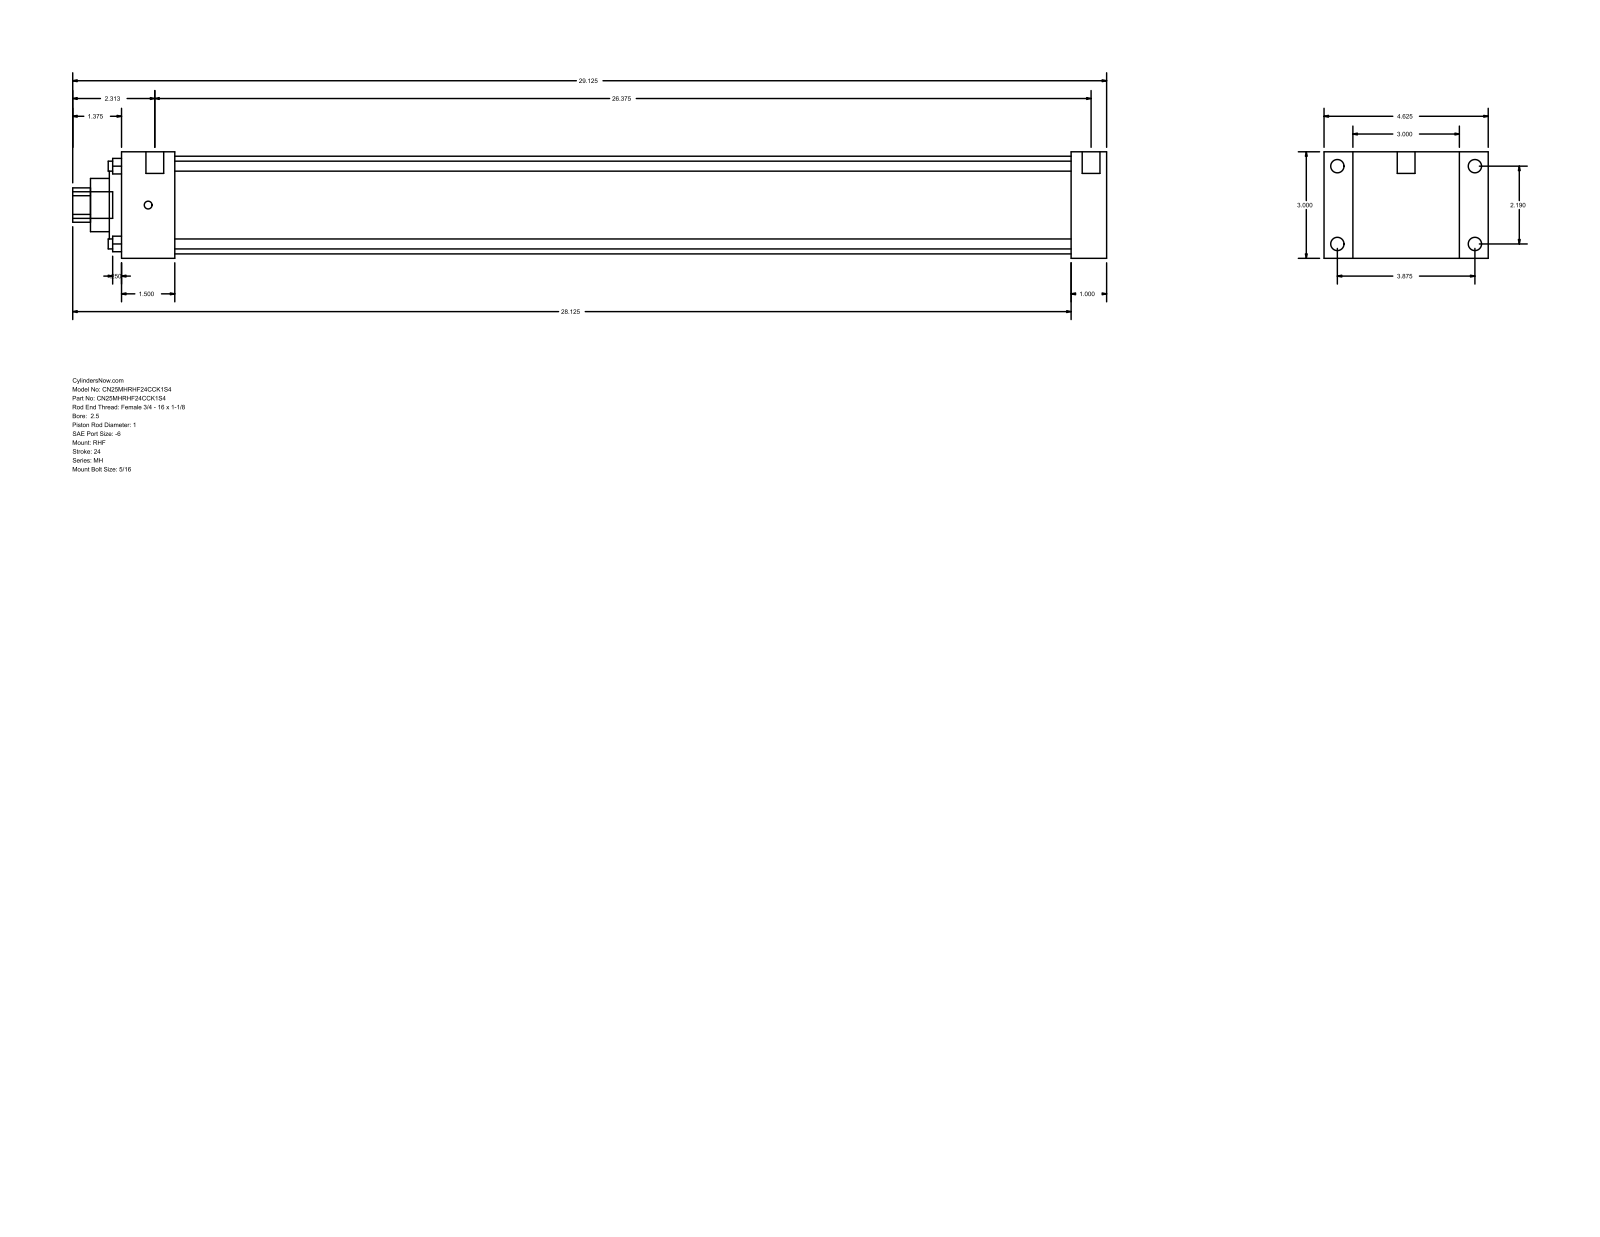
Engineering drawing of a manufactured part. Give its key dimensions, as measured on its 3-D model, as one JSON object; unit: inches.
{"part_name": "MH_RHF__0250_1", "step_written_by": "GSSL Pune (CONFIG_CONTROL_DESIGN)", "units": "inches", "bodies": {"solids": 0, "faces": 90, "planar": 61, "cylindrical": 29, "other": 0}, "overall_size": [29.125, 4.625, 3], "round_holes": [[0.281, 4], [1, 1], [1.5, 1], [2.375, 1], [2.75, 1]], "round_bosses_or_shafts": [[0.375, 4], [0.219, 4], [0.5, 2], [0.75, 1]], "partial_cylinders_radius": [[0.484, 1]], "face_to_face_distances": [3, 1, 0.813, 3.813, 27.75, 26.75, 4.625, 1.5, 25.25, 26.25], "hole_center_spacings": [1.548, 2.19, 3.097]}
